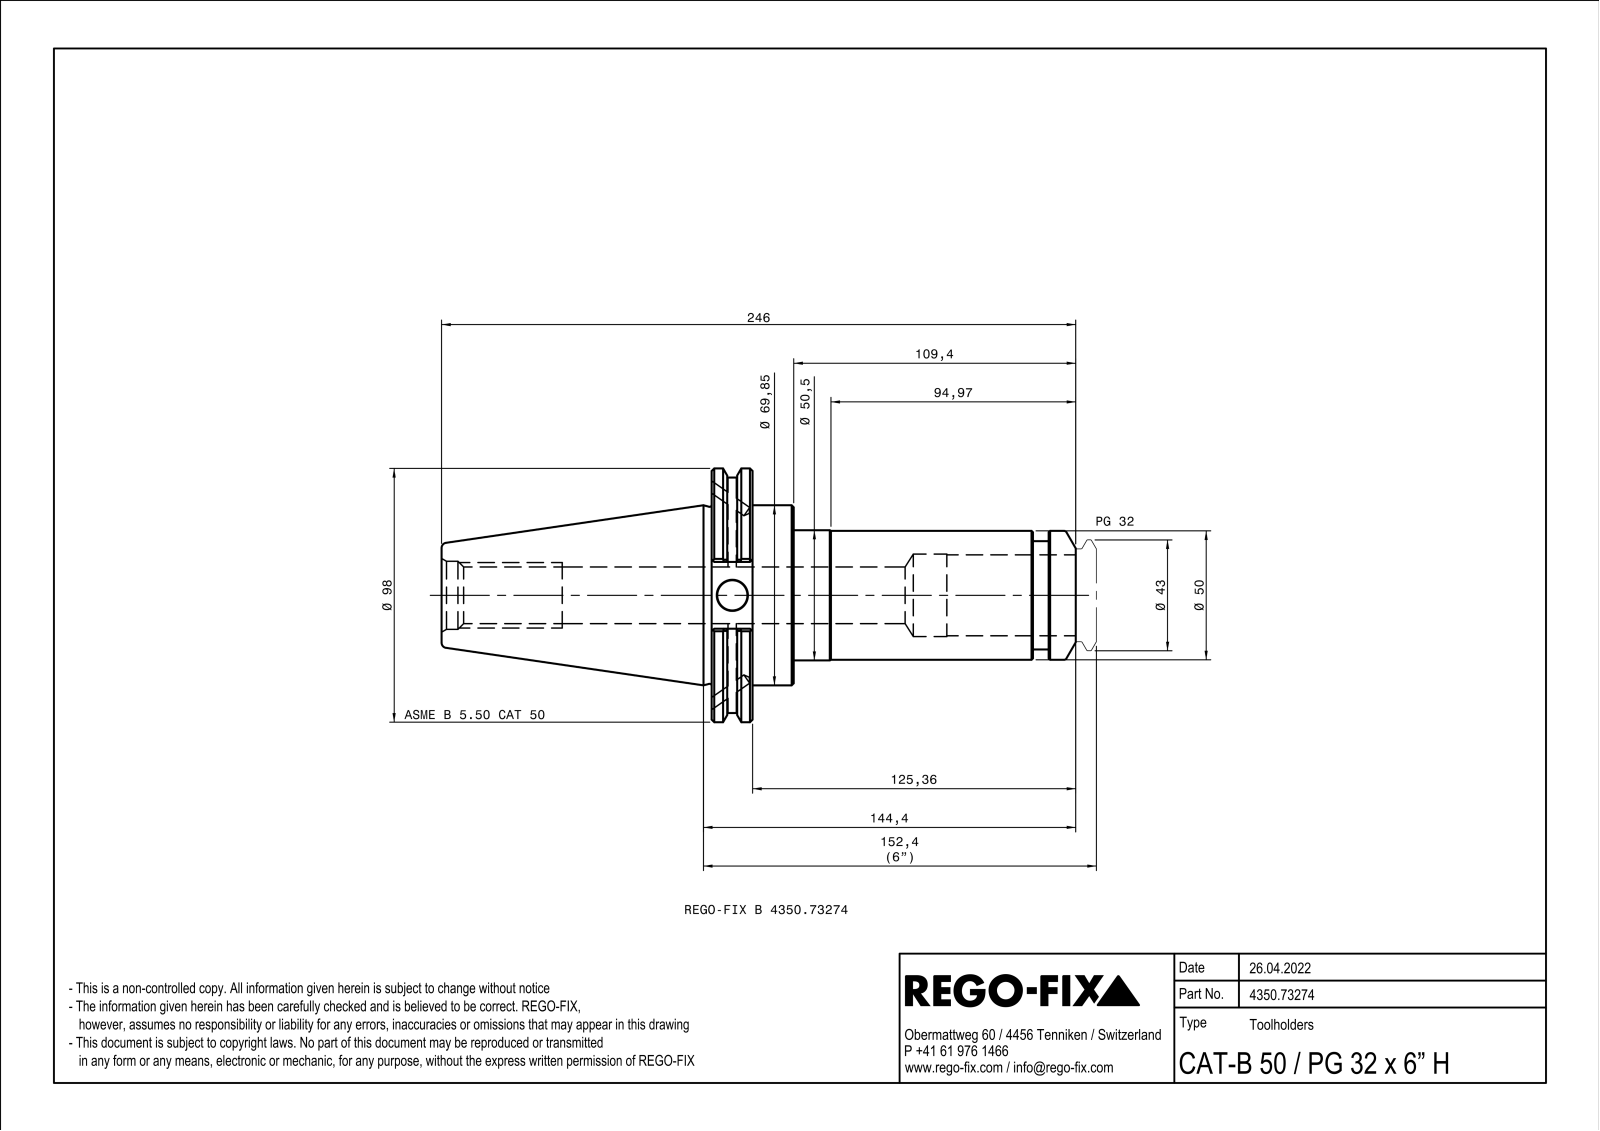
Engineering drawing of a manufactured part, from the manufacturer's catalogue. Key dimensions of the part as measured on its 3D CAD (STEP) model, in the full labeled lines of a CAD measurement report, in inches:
Part name (STEP PRODUCT): NOCUT
STEP written by: SIEMENS PLM Software Solid Edge ST10 (AUTOMOTIVE_DESIGN)
Units: inches
Bodies: 1 solid, 115 faces (34 planar, 31 cylindrical, 50 other)
Overall size (bounding box): 9.685 × 3.875 × 3.716
Volume: 31.3 in³ · Surface area: 116.9 in²
Round holes (diameter × count): ⌀0.461 ×1, ⌀0.865 ×1, ⌀1.039 ×1, ⌀1.299 ×1
Round bosses / shafts (diameter × count): ⌀3.875 ×1, ⌀3.594 ×1, ⌀2.75 ×1, ⌀1.988 ×1, ⌀1.969 ×1, ⌀1.654 ×1
Partial cylindrical surfaces — rounded edges, fillets, slot ends (radius × count): R0.02 ×12
Main face-to-face distances: 0.625, 0.628, 1.253, 3.654, 4.282, 4.907, 0.24, 3.894, 4.522, 5.147
